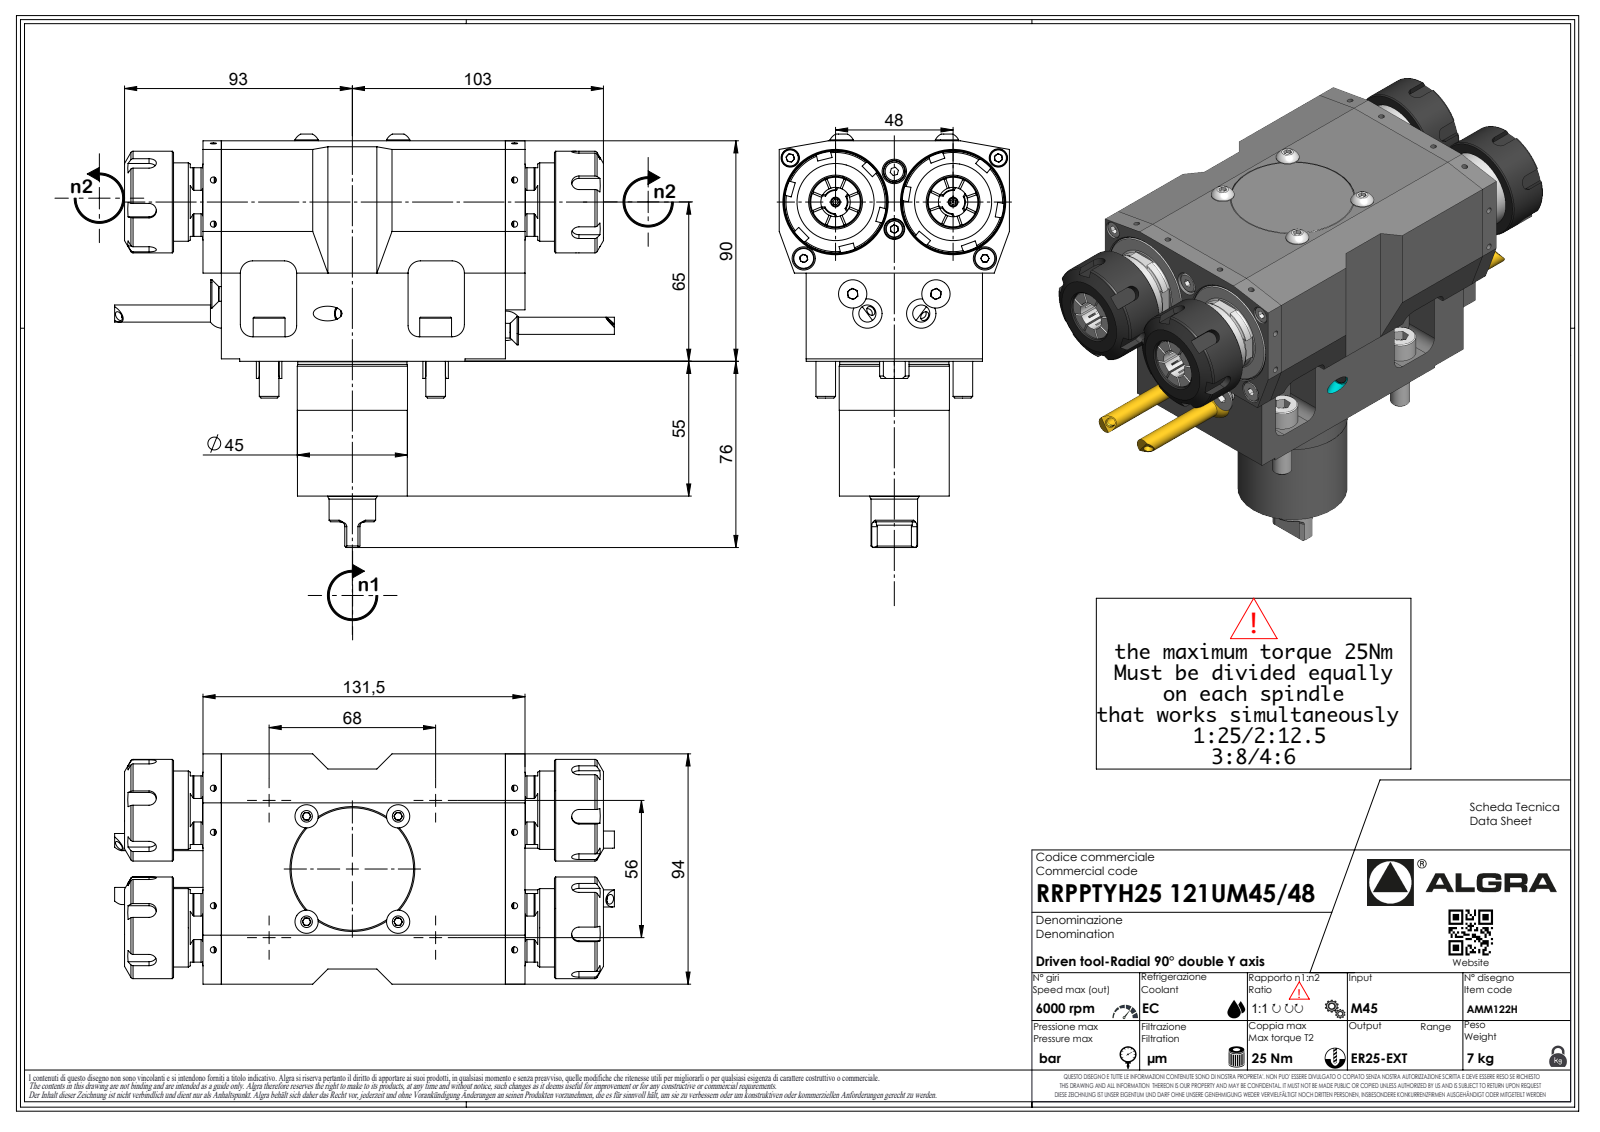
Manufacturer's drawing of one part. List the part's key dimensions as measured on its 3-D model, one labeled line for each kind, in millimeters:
Part name (STEP PRODUCT): RRPPTYH25121UM4548
STEP written by: SolidWorks 2023 (AUTOMOTIVE_DESIGN)
Units: millimetres
Bodies: 5 solids, 874 faces (537 planar, 138 cylindrical, 199 other)
Overall size (bounding box): 204.08 × 166 × 94
Volume: 1 292 000 mm³ · Surface area: 116 829 mm²
Round holes (diameter × count): ⌀4 ×4, ⌀5 ×2, ⌀2.1 ×1
Round bosses / shafts (diameter × count): ⌀8 ×4, ⌀7 ×4, ⌀41.5 ×2, ⌀32 ×2, ⌀45 ×1, ⌀44.85 ×1, ⌀20.3 ×1, ⌀19 ×1
Partial cylindrical surfaces — rounded edges, fillets, slot ends (radius × count): R3 ×24, R2 ×10, R0.33 ×7, R0.52 ×7, R3.7 ×7, R5 ×2, R6 ×2, R14.8 ×2
Main face-to-face distances: 11, 83, 12.03, 143.53, 20, 32.03, 163.53, 175.56, 90, 94
Hole centre spacings: 68
